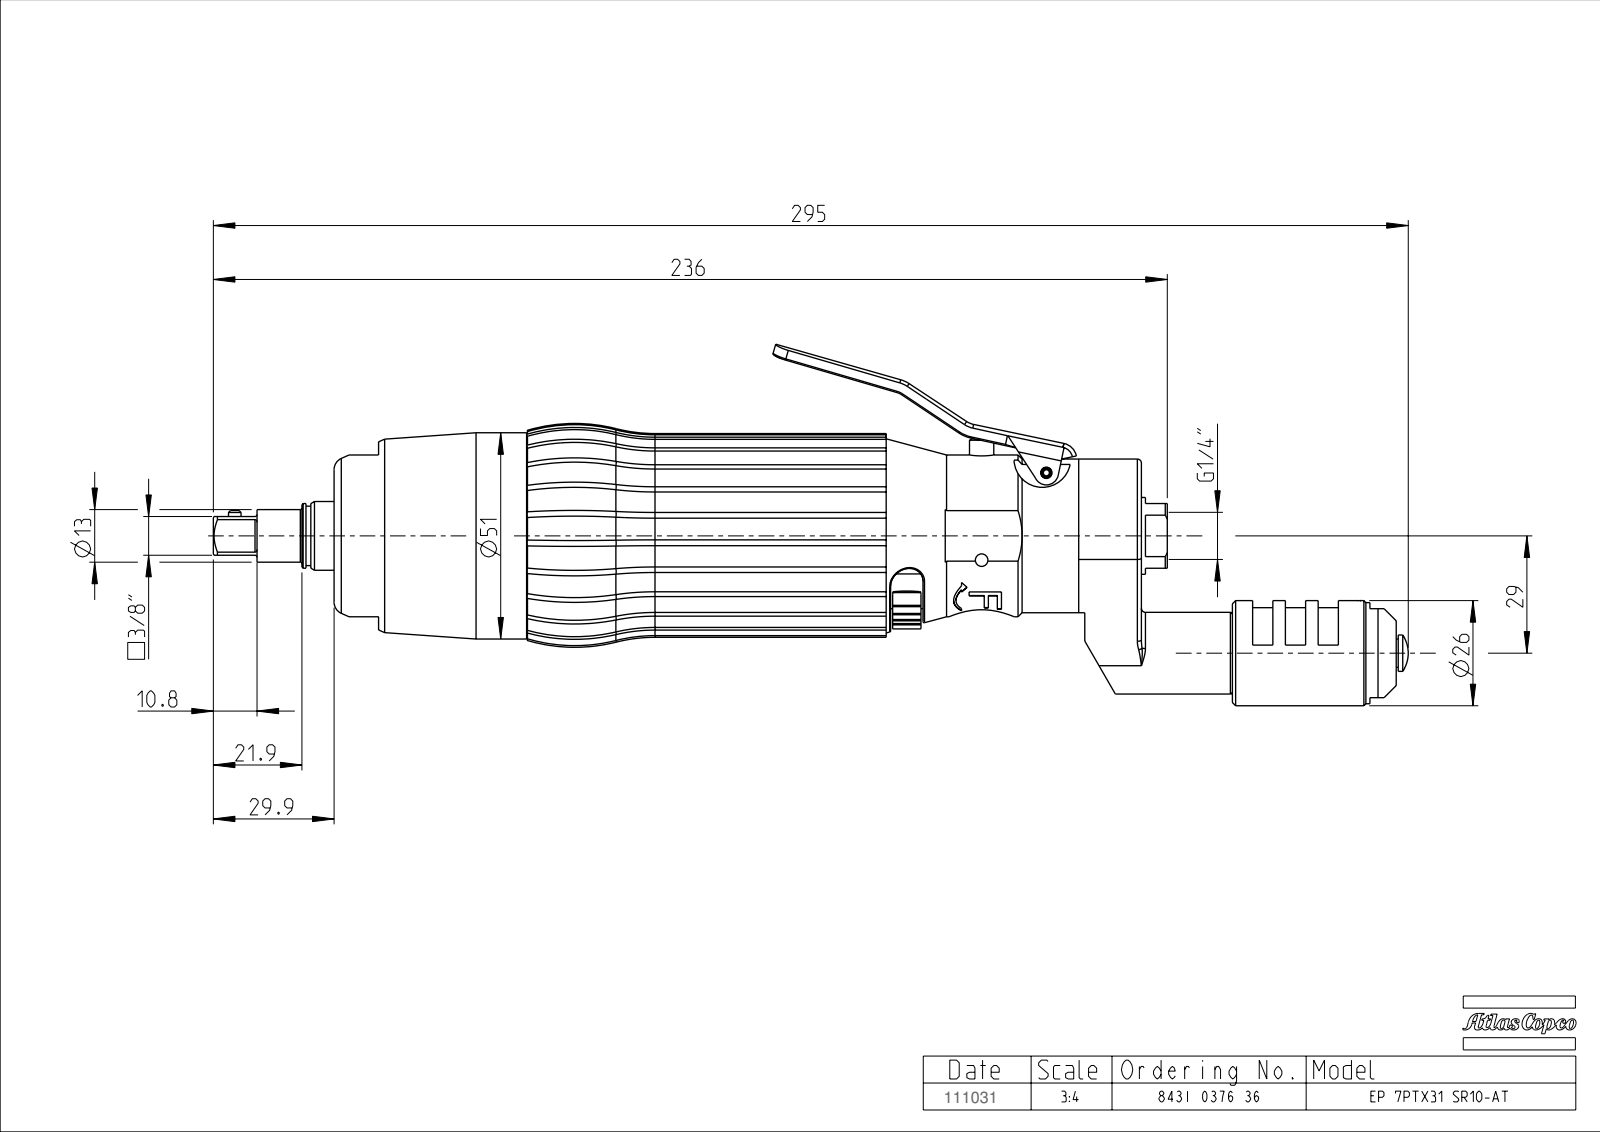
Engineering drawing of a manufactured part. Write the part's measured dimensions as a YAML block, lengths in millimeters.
part_name: "EXT_COMP_SW0006"
step_written_by: "CREO PARAMETRIC BY PTC INC, 2020281 (CONFIG_CONTROL_DESIGN)"
units: millimeters
bodies: {solids: 2, faces: 745, planar: 200, cylindrical: 172, other: 373}
overall_size: [292.9, 73, 58.9]
volume: 382100
surface_area: 53710
round_holes:
  - {diameter: 3.1, count: 2}
  - {diameter: 1.5, count: 1}
  - {diameter: 2, count: 1}
  - {diameter: 2.8, count: 1}
  - {diameter: 4.7, count: 1}
  - {diameter: 5.4, count: 1}
  - {diameter: 9.8, count: 1}
  - {diameter: 11.7, count: 1}
  - {diameter: 12, count: 1}
  - {diameter: 13, count: 1}
  - {diameter: 15.5, count: 1}
  - {diameter: 18.4, count: 1}
round_bosses_or_shafts:
  - {diameter: 15, count: 2}
  - {diameter: 51, count: 1}
  - {diameter: 40, count: 1}
  - {diameter: 38, count: 1}
  - {diameter: 26, count: 1}
  - {diameter: 25, count: 1}
  - {diameter: 23, count: 1}
  - {diameter: 20.2, count: 1}
partial_cylinders:
  - {radius: 1, count: 25}
  - {radius: 0.3, count: 8}
  - {radius: 0.5, count: 6}
  - {radius: 3.5, count: 4}
  - {radius: 2, count: 3}
  - {radius: 1.8, count: 2}
  - {radius: 4, count: 2}
  - {radius: 3, count: 1}
face_to_face_distances: [199.6, 137.6, 40.5, 38.5, 37, 48, 77.5, 1, 40, 1.5]
hole_center_spacings: [2.5, 26.9, 29, 31, 100.8, 117.6, 184.7]
